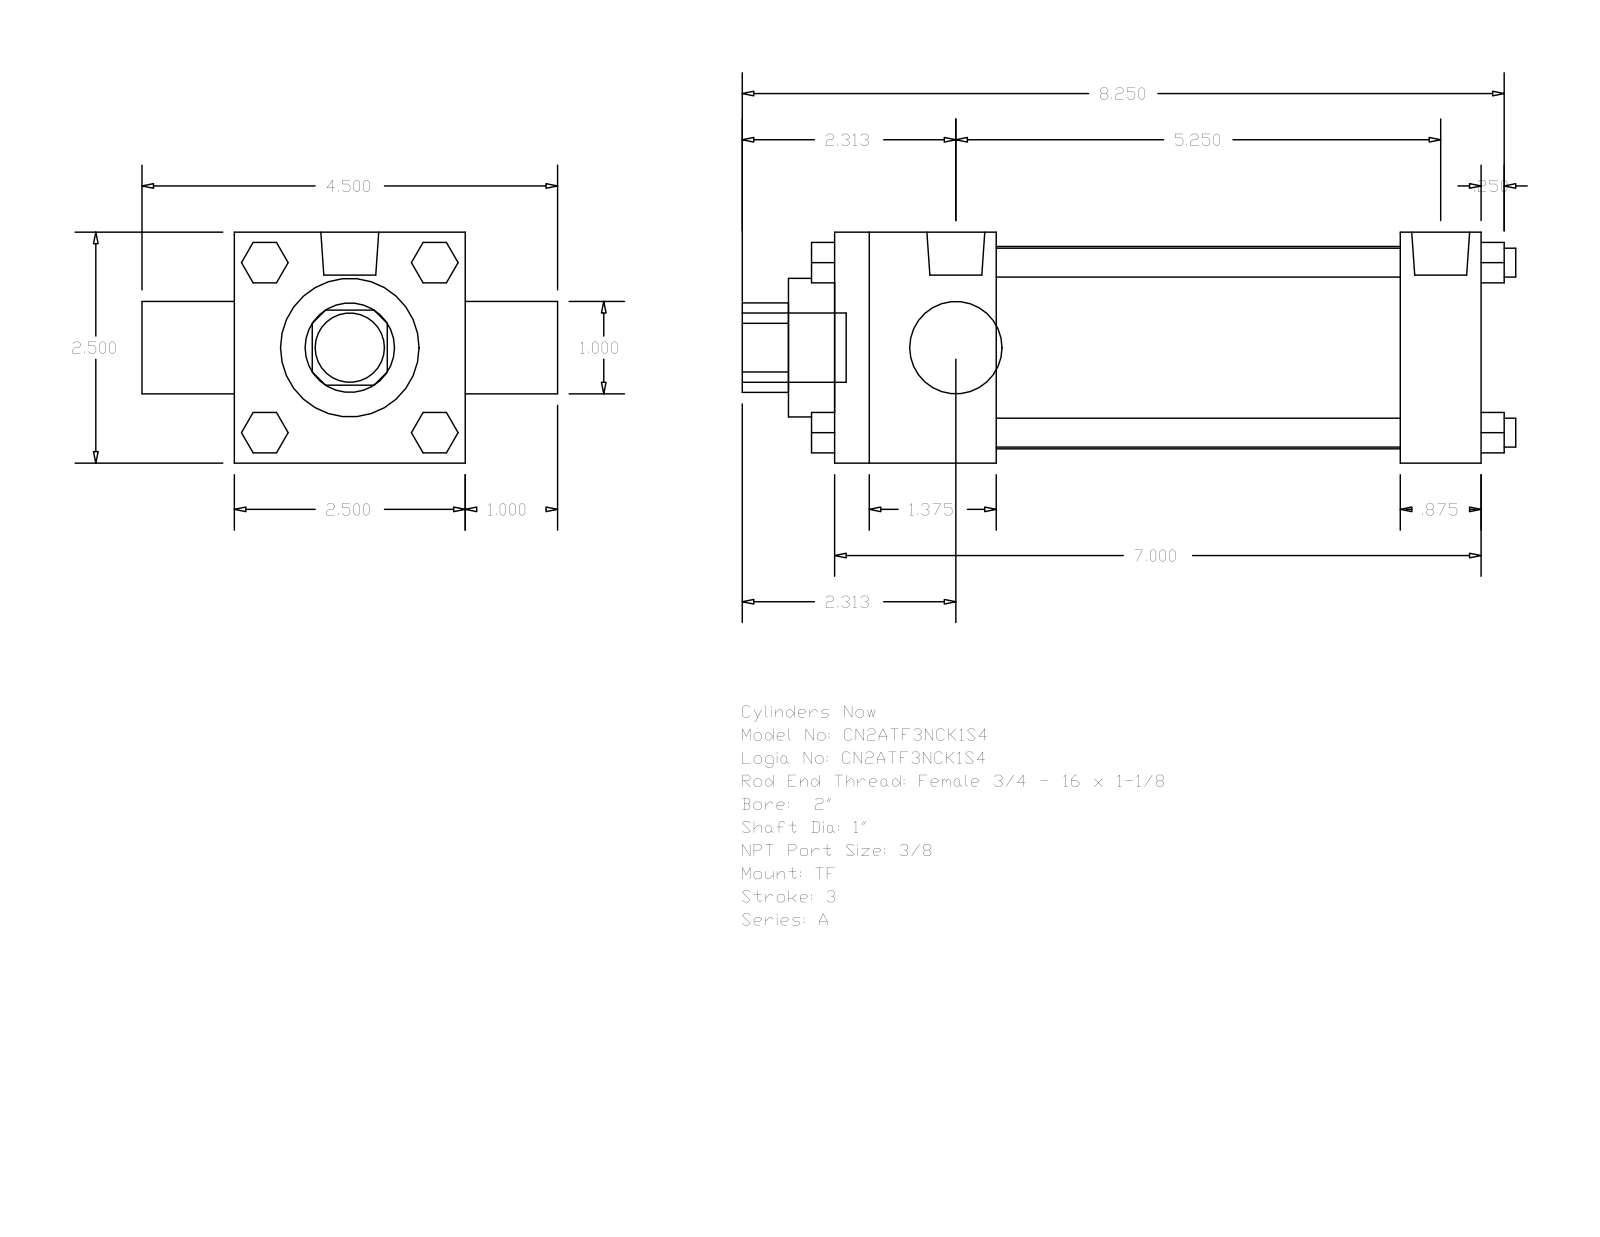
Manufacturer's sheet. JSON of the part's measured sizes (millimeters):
{"part_name": "A_TF__0200_1", "step_written_by": "GSSL Pune (CONFIG_CONTROL_DESIGN)", "units": "millimeters", "bodies": {"solids": 0, "faces": 120, "planar": 92, "cylindrical": 28, "other": 0}, "overall_size": [212.72, 114.3, 63.5], "round_holes": [[25.4, 2], [38.1, 1], [55.63, 1]], "round_bosses_or_shafts": [[7.94, 4], [5.56, 3], [15.93, 2], [19.05, 1]], "partial_cylinders_radius": [[12.29, 1]], "face_to_face_distances": [63.5, 177.8, 44.45, 155.57, 111.12, 133.35, 22.23, 25.4, 88.9, 190.5]}
